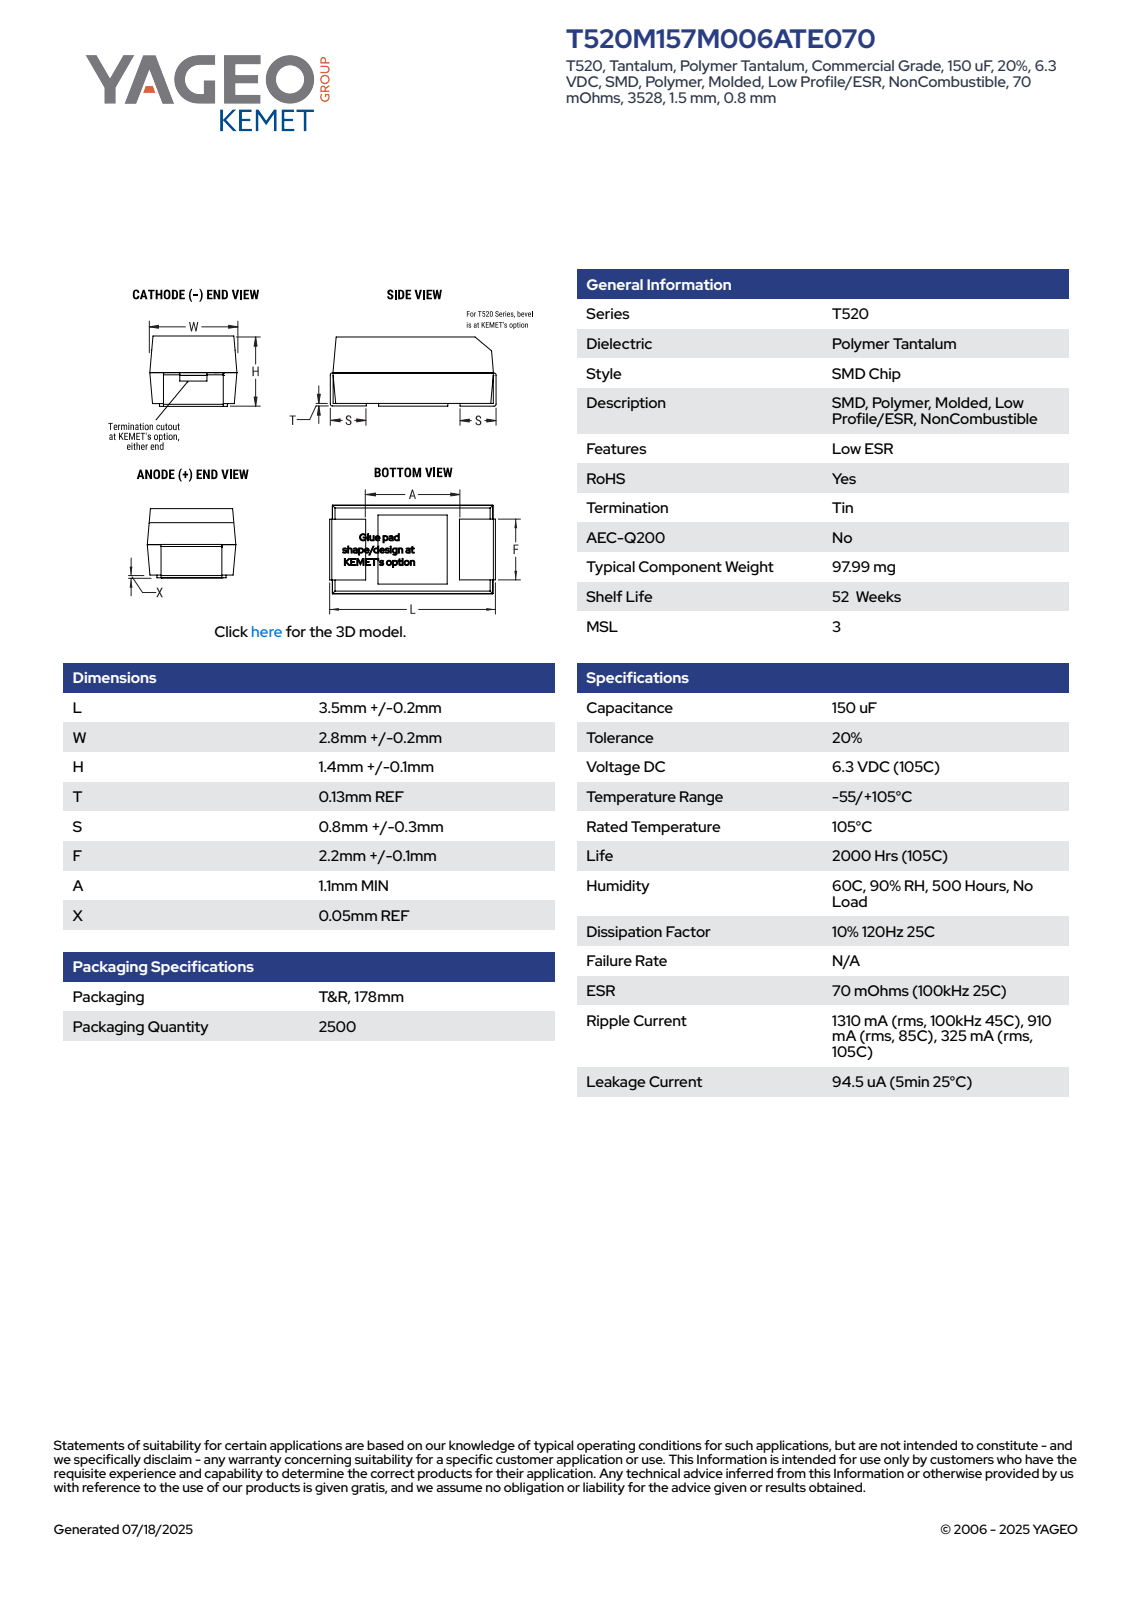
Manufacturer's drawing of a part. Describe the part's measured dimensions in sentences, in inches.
The part is named "CTS_TCM2NOBNOKBOPT_3528_L3.7W3H1.5T0.13S0.8F2.3A1.1X0.05". Its 3-D file was written by "SolidWorks 2014 (AUTOMOTIVE_DESIGN)". It is 4 solids with 90 faces: 86 planar, 4 cylindrical and 0 other. Overall it measures 0.146 by 0.118 by 0.059 inches. Its volume is 0.001 cubic inches and its surface area 0.071 square inches. Partial cylindrical surfaces (rounded edges, fillets, slot ends): 4 of radius 0.005. The main face-to-face distances are 0.056, 0.117, 0.059, 0.141, 0.054, 0.134, 0.134, 0.135, 0.146, 0.031.
